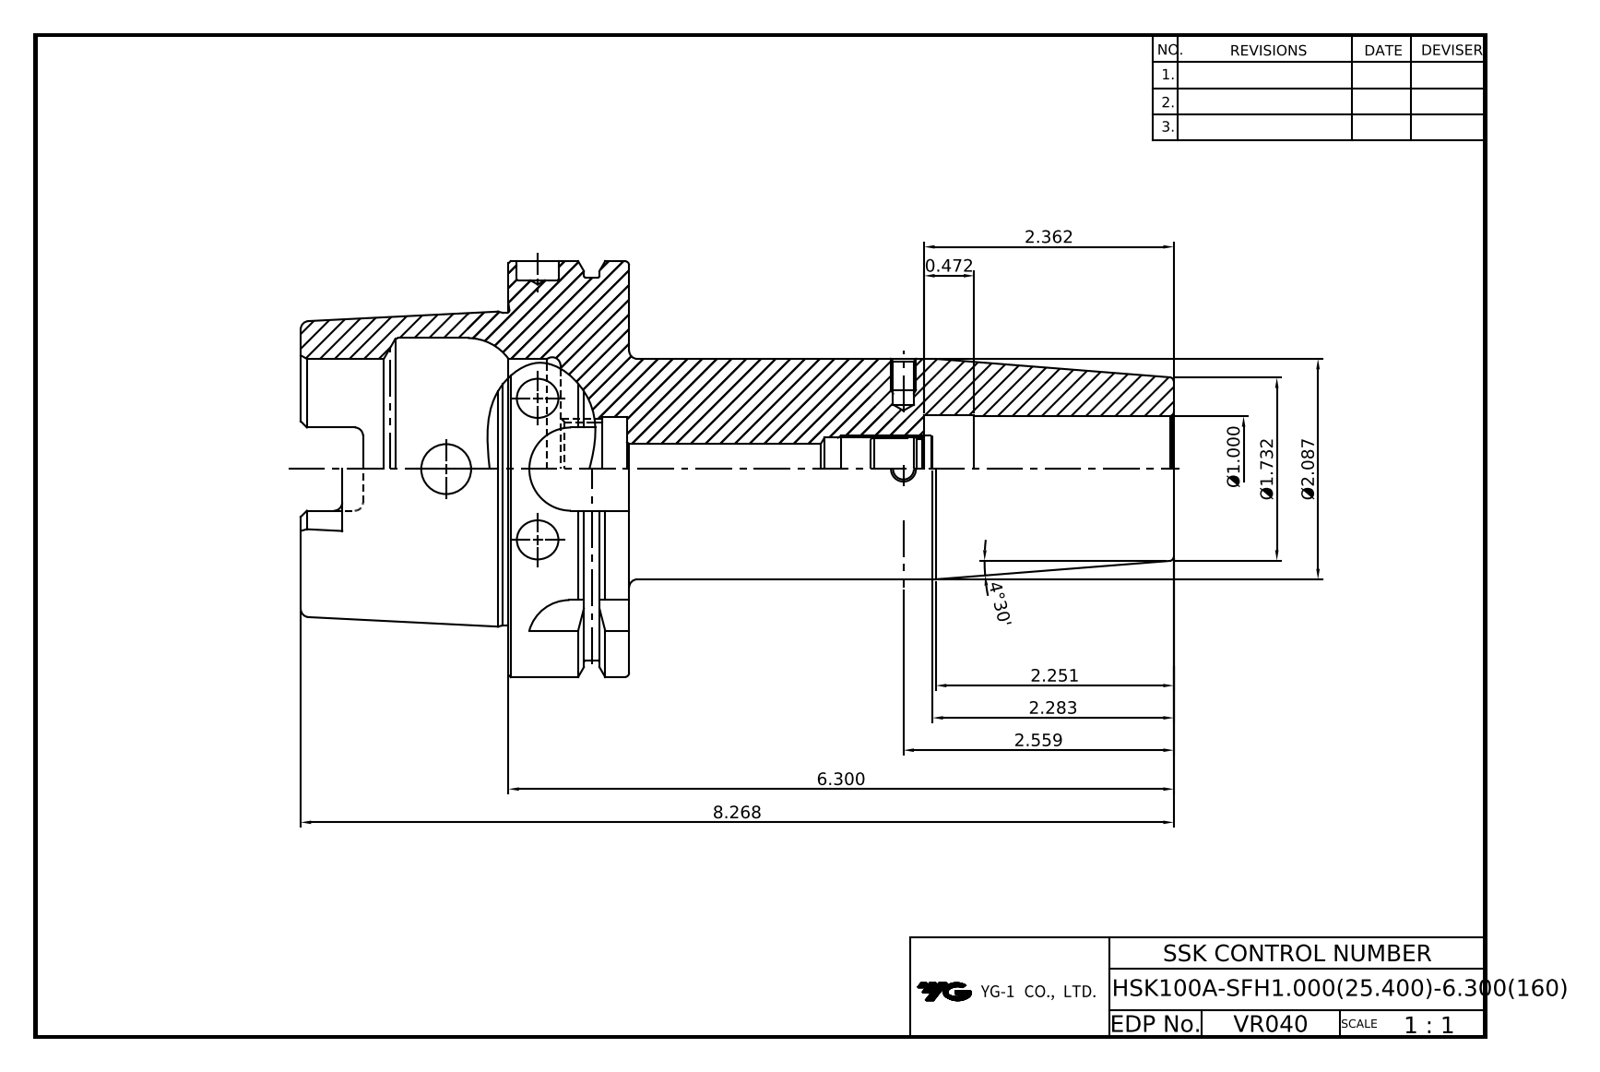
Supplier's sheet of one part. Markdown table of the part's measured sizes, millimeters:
| quantity | value |
| --- | --- |
| part name | HSK100A |
| STEP written by | CREO PARAMETRIC BY PTC INC, 2018400 (CONFIG_CONTROL_DESIGN) |
| units | millimeters |
| bodies | 1 solid, 212 faces (56 planar, 70 cylindrical, 86 other) |
| overall size | 165 × 100 × 100 |
| volume | 385 038 mm³ |
| surface area | 70 591 mm² |
| round holes (diameter × count) | 5 × 2, 6 × 2, 12 × 2, 10 × 1, 15.1 × 1, 22.5 × 1, 24 × 1, 25 × 1, 25.4 × 1, 26 × 1, 53 × 1, 63.96 × 1 |
| round bosses / shafts (diameter × count) | 100 × 1, 92 × 1, 75.16 × 1 |
| partial cylindrical surfaces (radius × count) | 2 × 6, 4.88 × 4, 10 × 4 |
| main face-to-face distances | 29, 12.5, 16.5, 62.5, 50, 79, 165, 115, 102.5, 86 |
| hole center spacings | 43, 65 |
